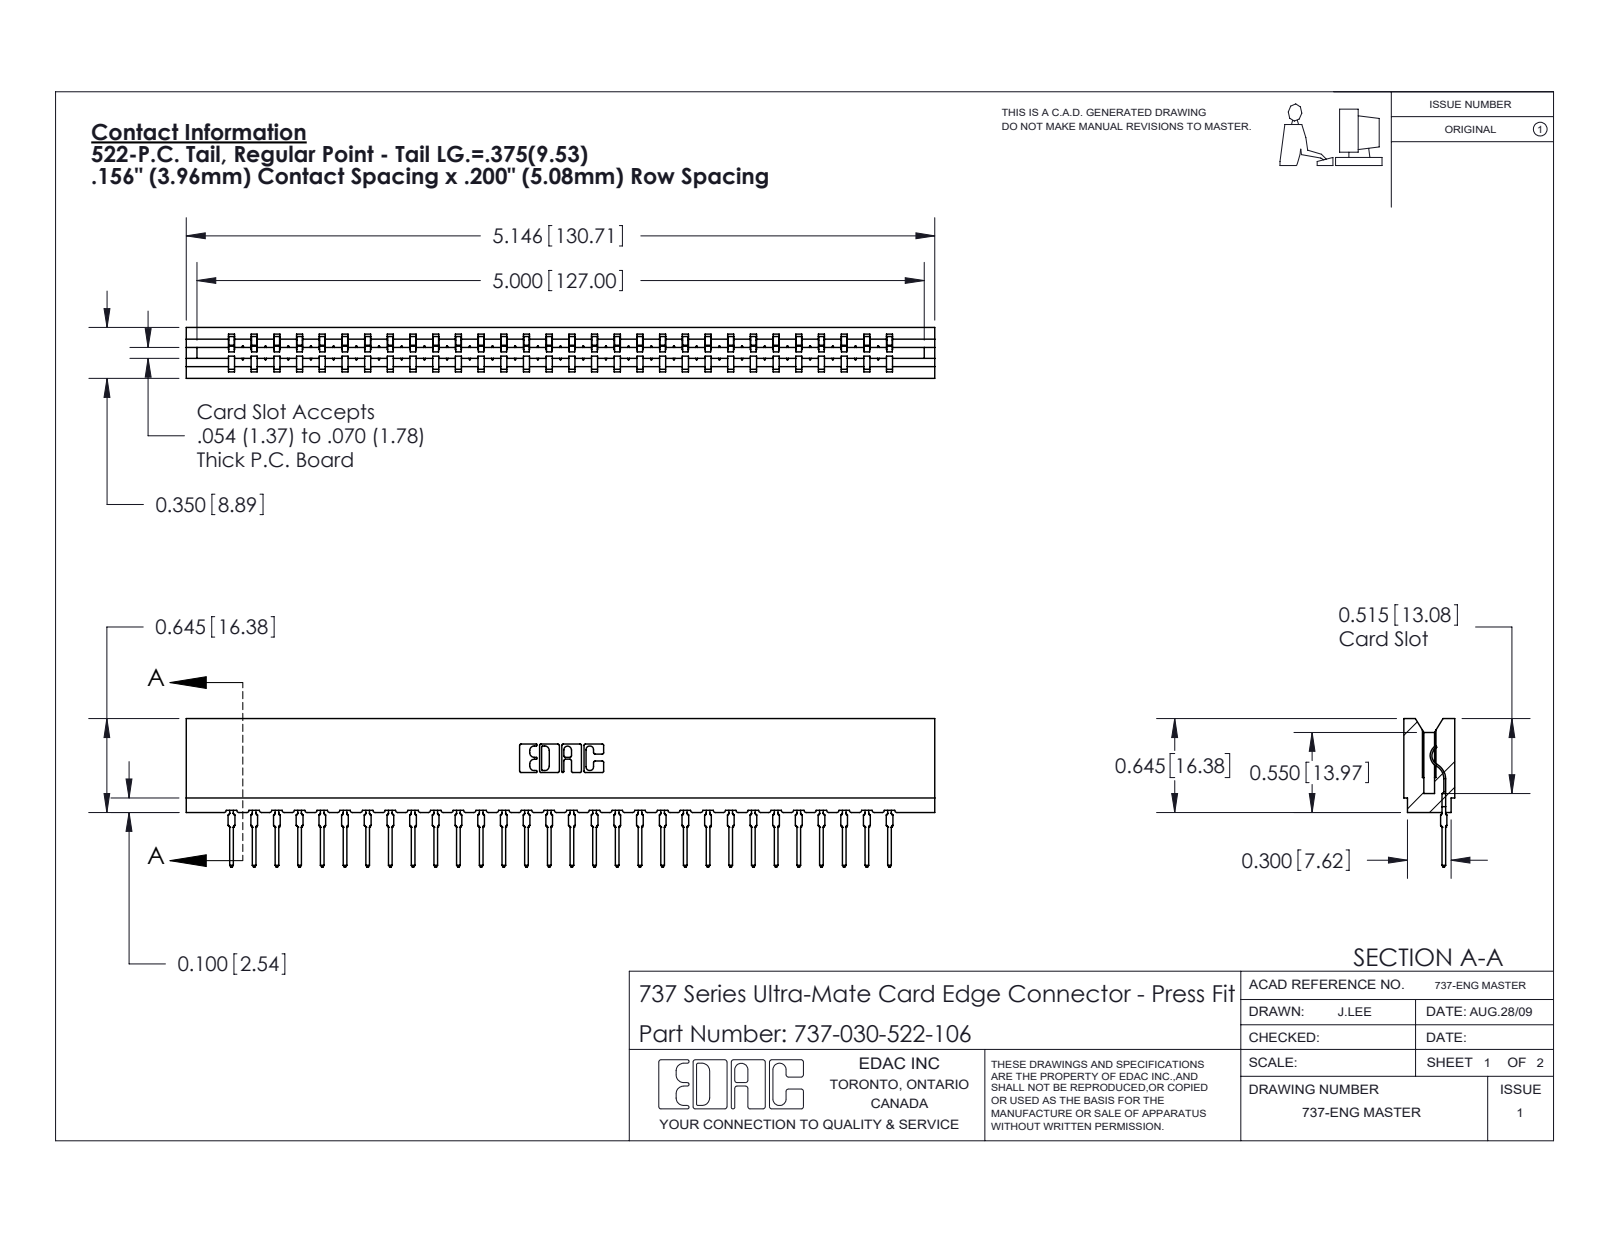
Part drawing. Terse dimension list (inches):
name: 737 Part_Insulator Option - 06; 737-030-522-106; 745-292-001_522
written by: SolidWorks 2020 (CONFIG_CONTROL_DESIGN)
unit: in
bodies: 31 solids, 3485 faces (2095 planar, 610 cylindrical, 780 other)
size: 5.146 × 1.021 × 0.35
volume: 0.776 in³; area: 26.26 in²
rounds: 60× R0.015, 60× R0.021, 22× R0.01, 6× R0.007, 6× R0.031, 4× R0.005, 4× R0.011, 3× R0.026
face distances: 0.138, 0.212, 0.35, 0.624, 0.074, 0.045, 0.305, 0.093, 0.167, 0.156
